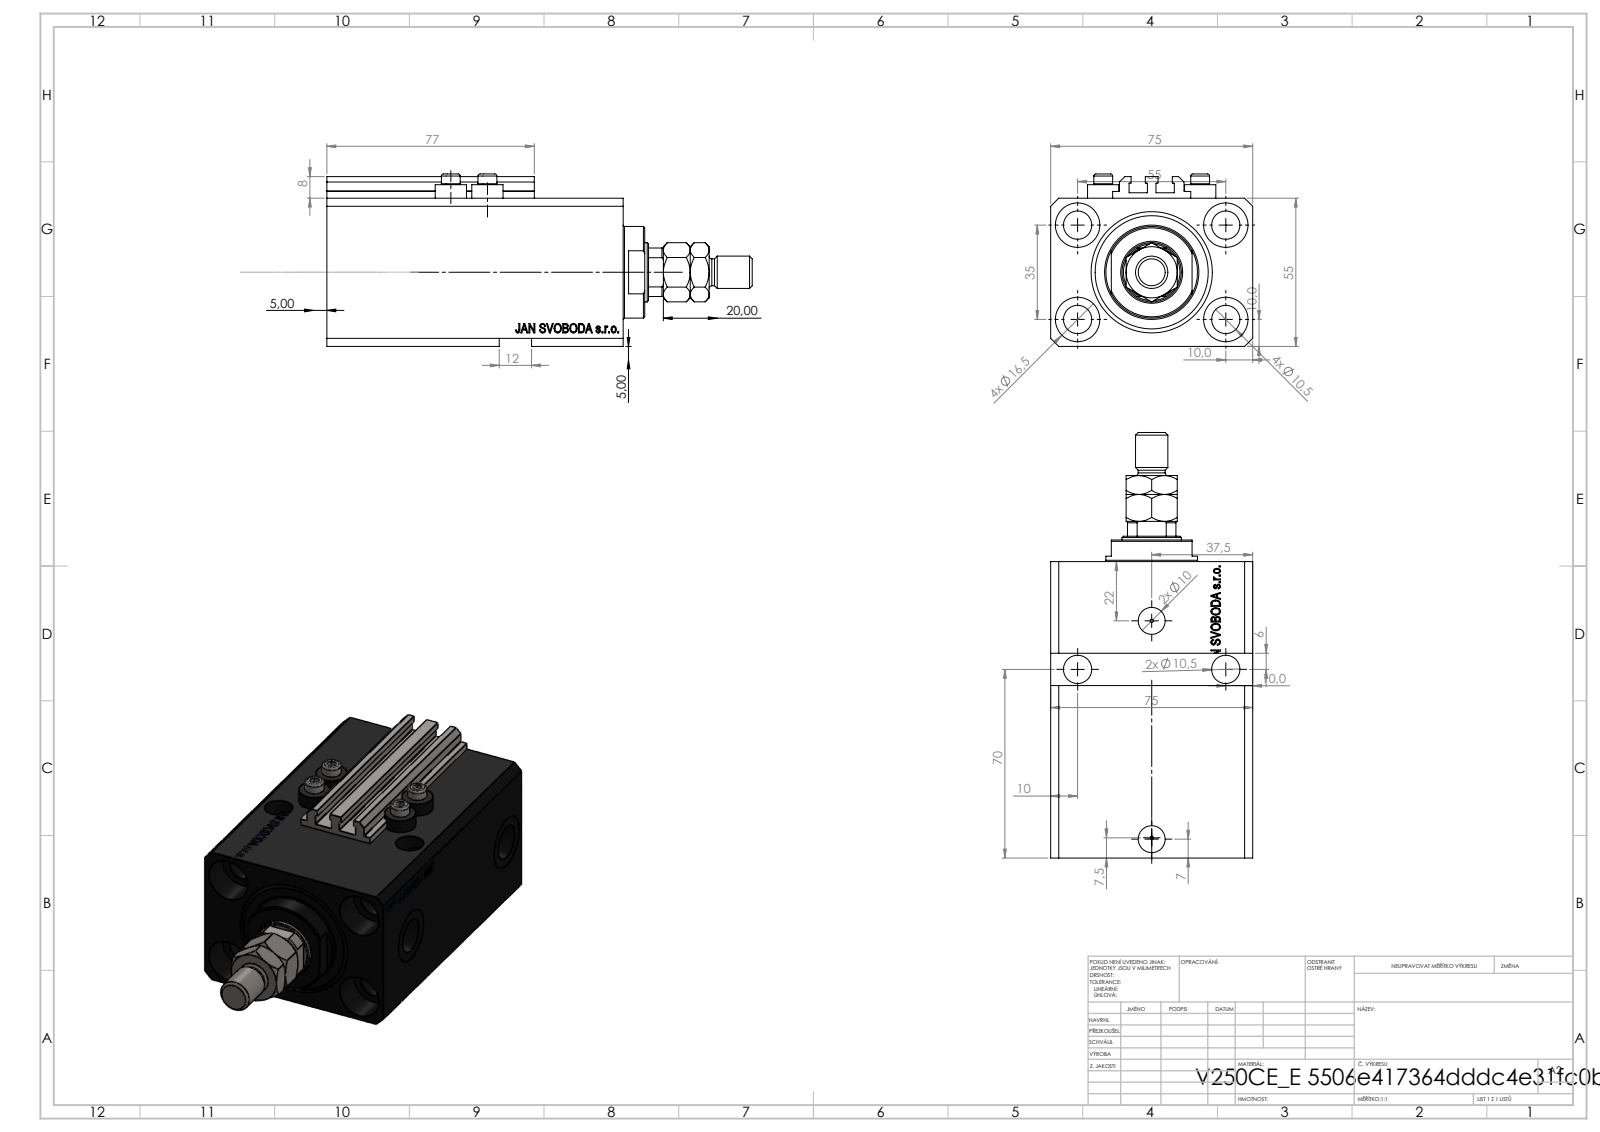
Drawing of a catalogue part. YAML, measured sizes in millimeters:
part_name: "MTA; V250CE_E_Body; V250CE_VC_E; ALLEN BOLT V250CE (+1 more)"
step_written_by: "SolidWorks 2019 (CONFIG_CONTROL_DESIGN)"
units: millimeters
bodies: {solids: 9, faces: 1133, planar: 529, cylindrical: 150, other: 454}
overall_size: [158, 75, 64]
volume: 388313
surface_area: 97960
round_holes:
  - {diameter: 10.5, count: 9}
  - {diameter: 1.25, count: 4}
  - {diameter: 4, count: 4}
  - {diameter: 16.5, count: 4}
  - {diameter: 10, count: 2}
  - {diameter: 13.16, count: 2}
  - {diameter: 20, count: 2}
  - {diameter: 22, count: 1}
  - {diameter: 32, count: 1}
  - {diameter: 45, count: 1}
round_bosses_or_shafts:
  - {diameter: 11.6, count: 4}
  - {diameter: 7, count: 4}
  - {diameter: 34, count: 1}
  - {diameter: 12, count: 1}
  - {diameter: 10, count: 1}
partial_cylinders:
  - {radius: 0.2, count: 10}
  - {radius: 10.5, count: 1}
face_to_face_distances: [55, 75, 15, 110, 95, 3, 9.9, 85.1, 100.1, 2.5]
hole_center_spacings: [32.6, 32.87, 55, 68.74, 13.6, 14.09, 23.05, 25.81]
